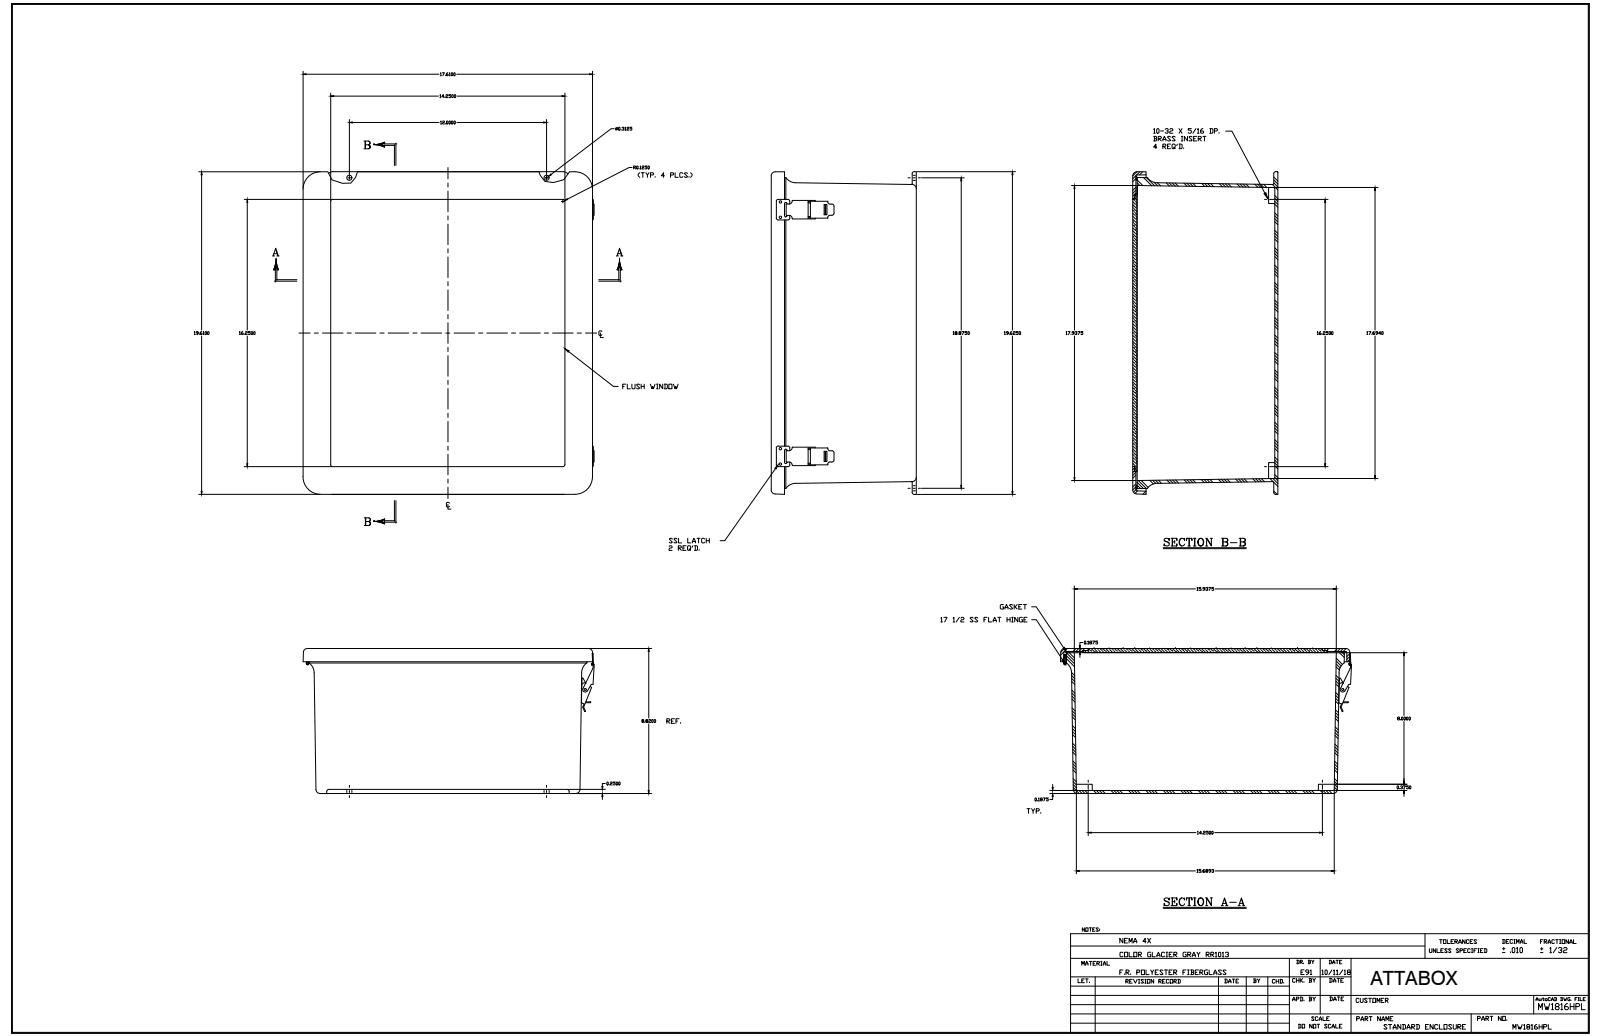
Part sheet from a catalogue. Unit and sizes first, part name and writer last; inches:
Units: inches
Overall size (bounding box): 19.625 × 17.706 × 8.812
Round holes (diameter × count): ⌀0.14 ×24, ⌀0.131 ×12, ⌀0.104 ×8, ⌀0.152 ×5, ⌀0.13 ×4, ⌀0.156 ×4, ⌀0.218 ×4, ⌀0.135 ×2, ⌀0.375 ×2, ⌀0.085 ×1, ⌀0.135 ×1
Round bosses / shafts (diameter × count): ⌀0.125 ×13, ⌀0.25 ×12, ⌀0.125 ×7, ⌀0.27 ×4, ⌀0.3 ×1, ⌀0.17 ×1, ⌀0.155 ×1, ⌀0.155 ×1
Partial cylindrical surfaces — rounded edges, fillets, slot ends (radius × count): R0.125 ×24, R0.015 ×20, R0.031 ×20, R0.045 ×16, R0.03 ×12, R0.25 ×12, R0.023 ×8, R0.06 ×6
Main face-to-face distances: 0.187, 8.812, 0.188, 0.25, 8.562, 8.624, 8.374, 8.624, 8.437, 0.063
Hole centre spacings: 3.375, 3.375, 6.75, 10.25, 14.984, 0.25, 10, 14.984
Volume: 276 in³ · Surface area: 2 796 in²
Bodies: 43 solids, 1160 faces (524 planar, 485 cylindrical, 151 other)
Part name (STEP PRODUCT): MW1816HPL
STEP written by: SolidWorks 2018 (AUTOMOTIVE_DESIGN)
